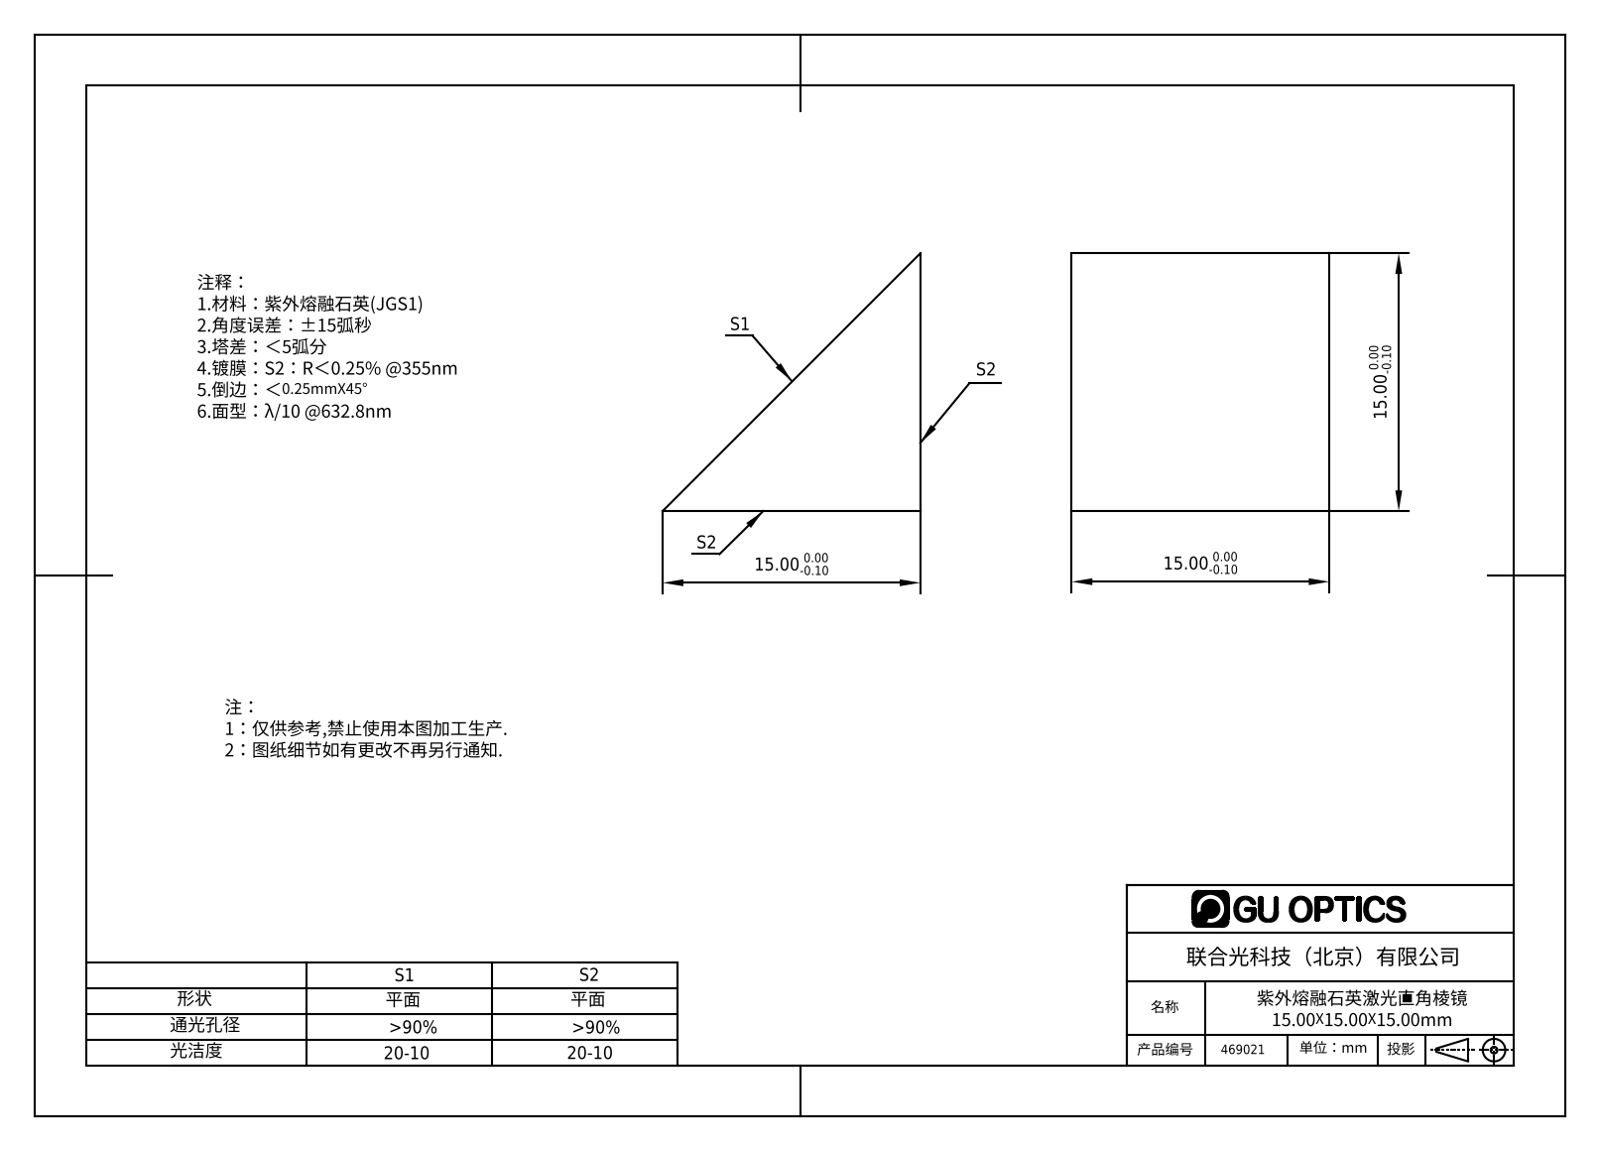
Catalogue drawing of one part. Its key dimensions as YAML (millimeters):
part_name: "469003"
step_written_by: "SolidWorks 2016 (AUTOMOTIVE_DESIGN)"
units: millimeters
bodies: {solids: 1, faces: 5, planar: 5, cylindrical: 0, other: 0}
overall_size: [18.82, 15, 12.51]
volume: 1652
surface_area: 954
face_to_face_distances: [15]
